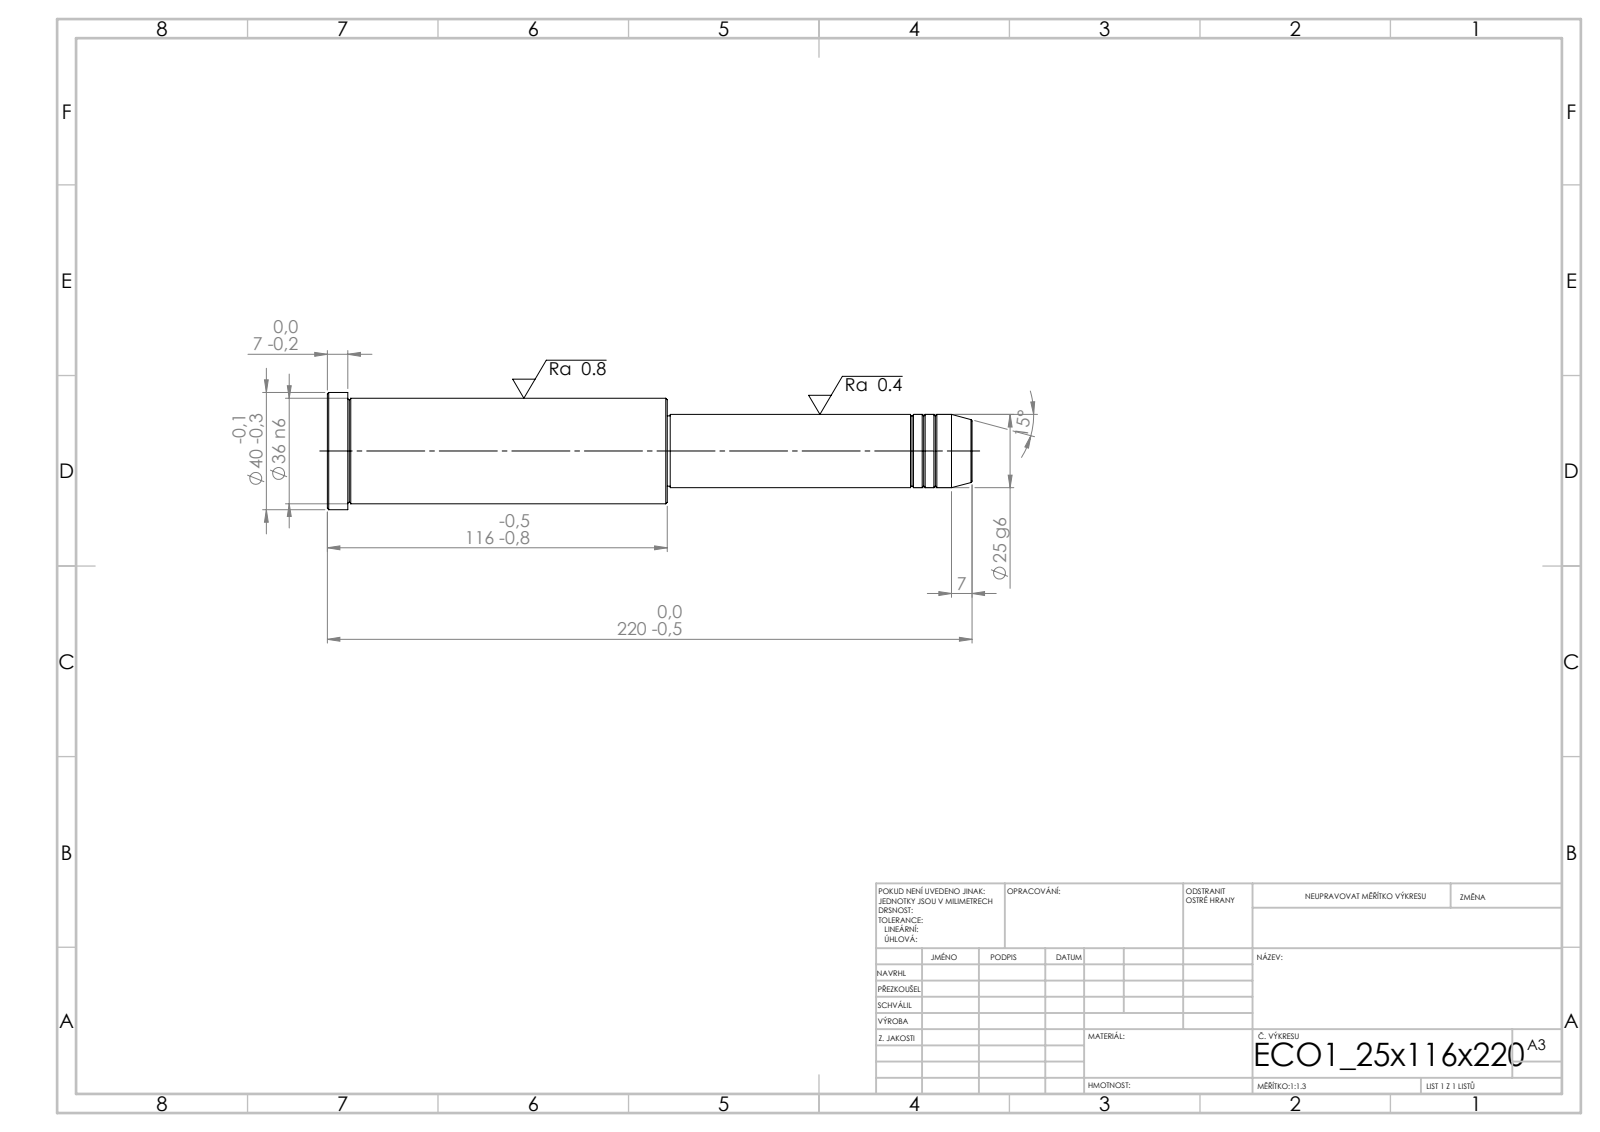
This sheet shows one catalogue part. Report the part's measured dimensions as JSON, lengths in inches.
{"step_written_by": "SolidWorks 2019 (CONFIG_CONTROL_DESIGN)", "units": "inches", "bodies": {"solids": 1, "faces": 43, "planar": 5, "cylindrical": 14, "other": 24}, "overall_size": [8.661, 1.575, 1.575], "volume_in3": 10.38, "surface_area_in2": 37.06, "round_bosses_or_shafts": [[1.575, 1], [1.417, 1], [0.984, 1], [0.945, 1]], "face_to_face_distances": [4.567, 4.094, 8.661, 8.386, 4.291, 0.276, 4.055, 0.039, 4.331, 4.606]}
